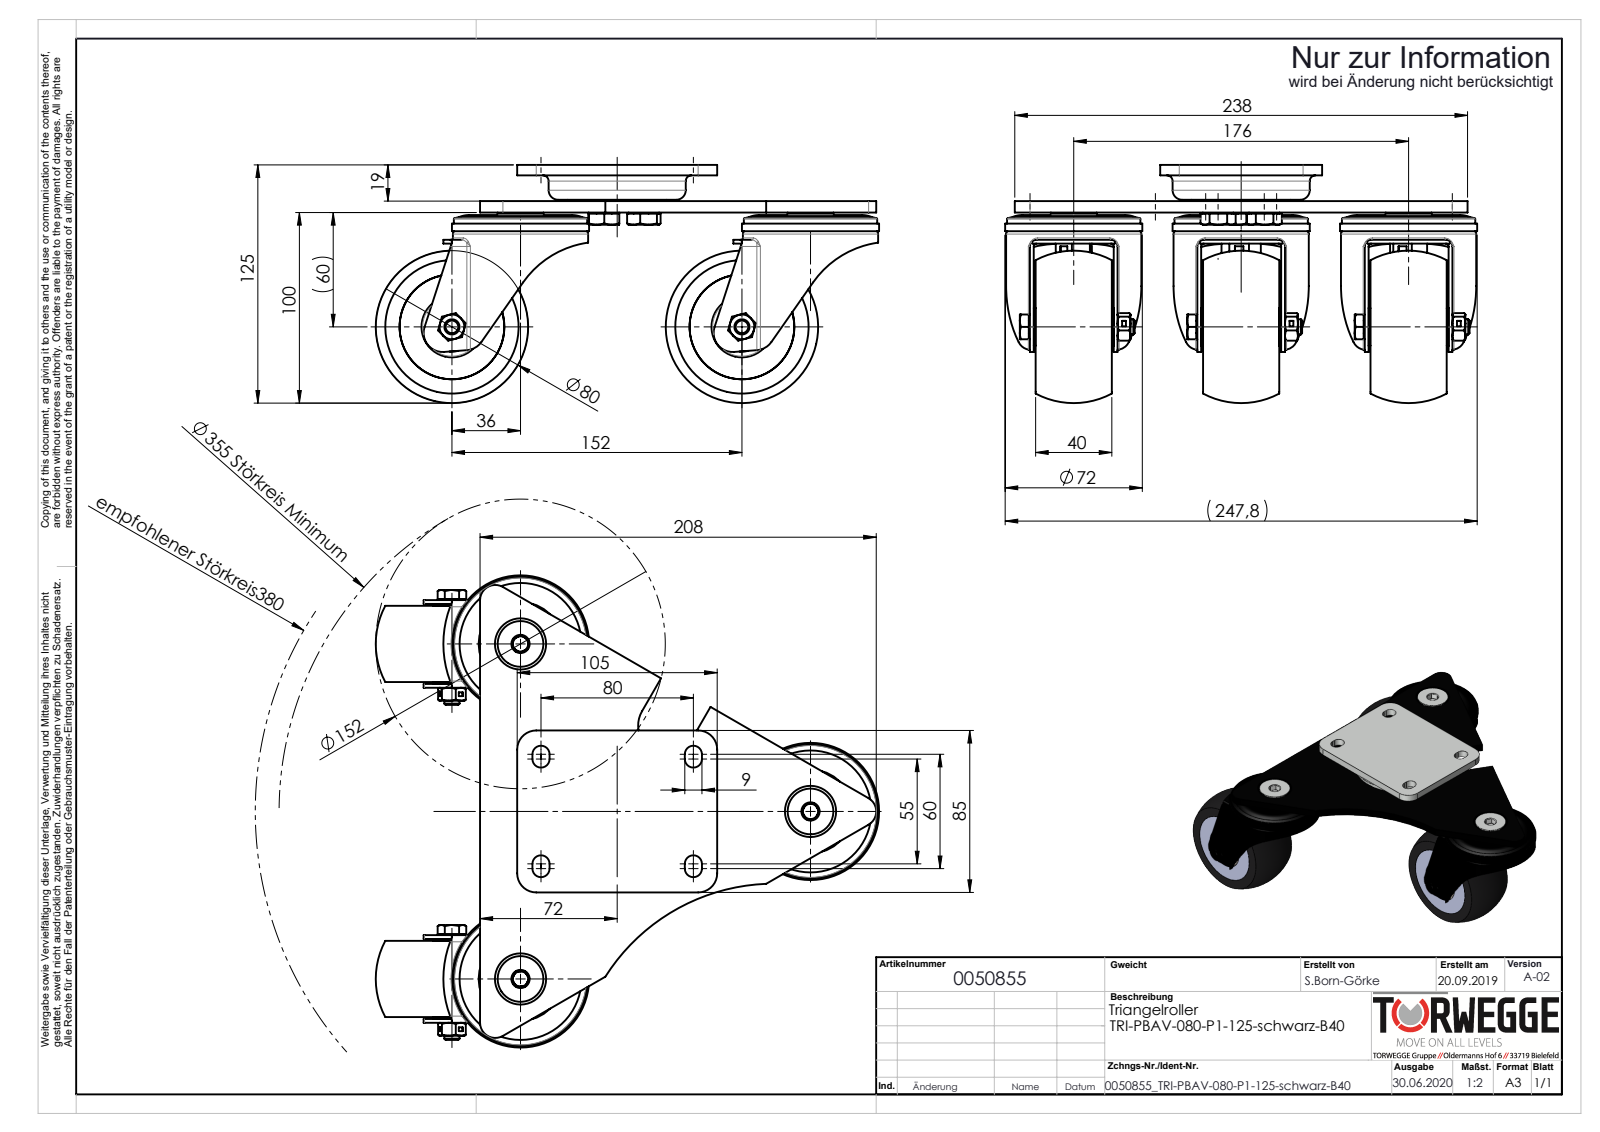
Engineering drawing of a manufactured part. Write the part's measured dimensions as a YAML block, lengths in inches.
part_name: "0050855"
step_written_by: "SolidWorks 2018 (AUTOMOTIVE_DESIGN)"
units: inches
bodies: {solids: 65, faces: 1335, planar: 463, cylindrical: 415, other: 457}
overall_size: [10.207, 9.756, 4.88]
volume: 57.06
surface_area: 539.1
round_holes:
  - {diameter: 0.472, count: 5}
  - {diameter: 0.335, count: 3}
  - {diameter: 0.402, count: 3}
  - {diameter: 0.512, count: 3}
  - {diameter: 0.551, count: 3}
  - {diameter: 2.638, count: 3}
  - {diameter: 0.268, count: 2}
  - {diameter: 0.315, count: 2}
  - {diameter: 0.323, count: 2}
  - {diameter: 0.488, count: 2}
  - {diameter: 0.709, count: 2}
  - {diameter: 1.024, count: 2}
round_bosses_or_shafts:
  - {diameter: 2.835, count: 4}
  - {diameter: 2.795, count: 3}
  - {diameter: 2.756, count: 3}
  - {diameter: 0.945, count: 3}
  - {diameter: 0.63, count: 3}
  - {diameter: 0.787, count: 2}
  - {diameter: 0.591, count: 2}
  - {diameter: 0.512, count: 2}
partial_cylinders:
  - {radius: 0.177, count: 14}
  - {radius: 0.394, count: 8}
  - {radius: 0.059, count: 6}
  - {radius: 0.098, count: 6}
  - {radius: 0.138, count: 6}
  - {radius: 0.236, count: 3}
  - {radius: 0.315, count: 3}
  - {radius: 2.181, count: 3}
face_to_face_distances: [0.236, 3.461, 0.602, 0.366, 0.079, 6.921, 1.575, 0.681, 0.445, 1.429]
hole_center_spacings: [4.298, 3.445, 6.921, 0.955, 0.954, 5.994]
